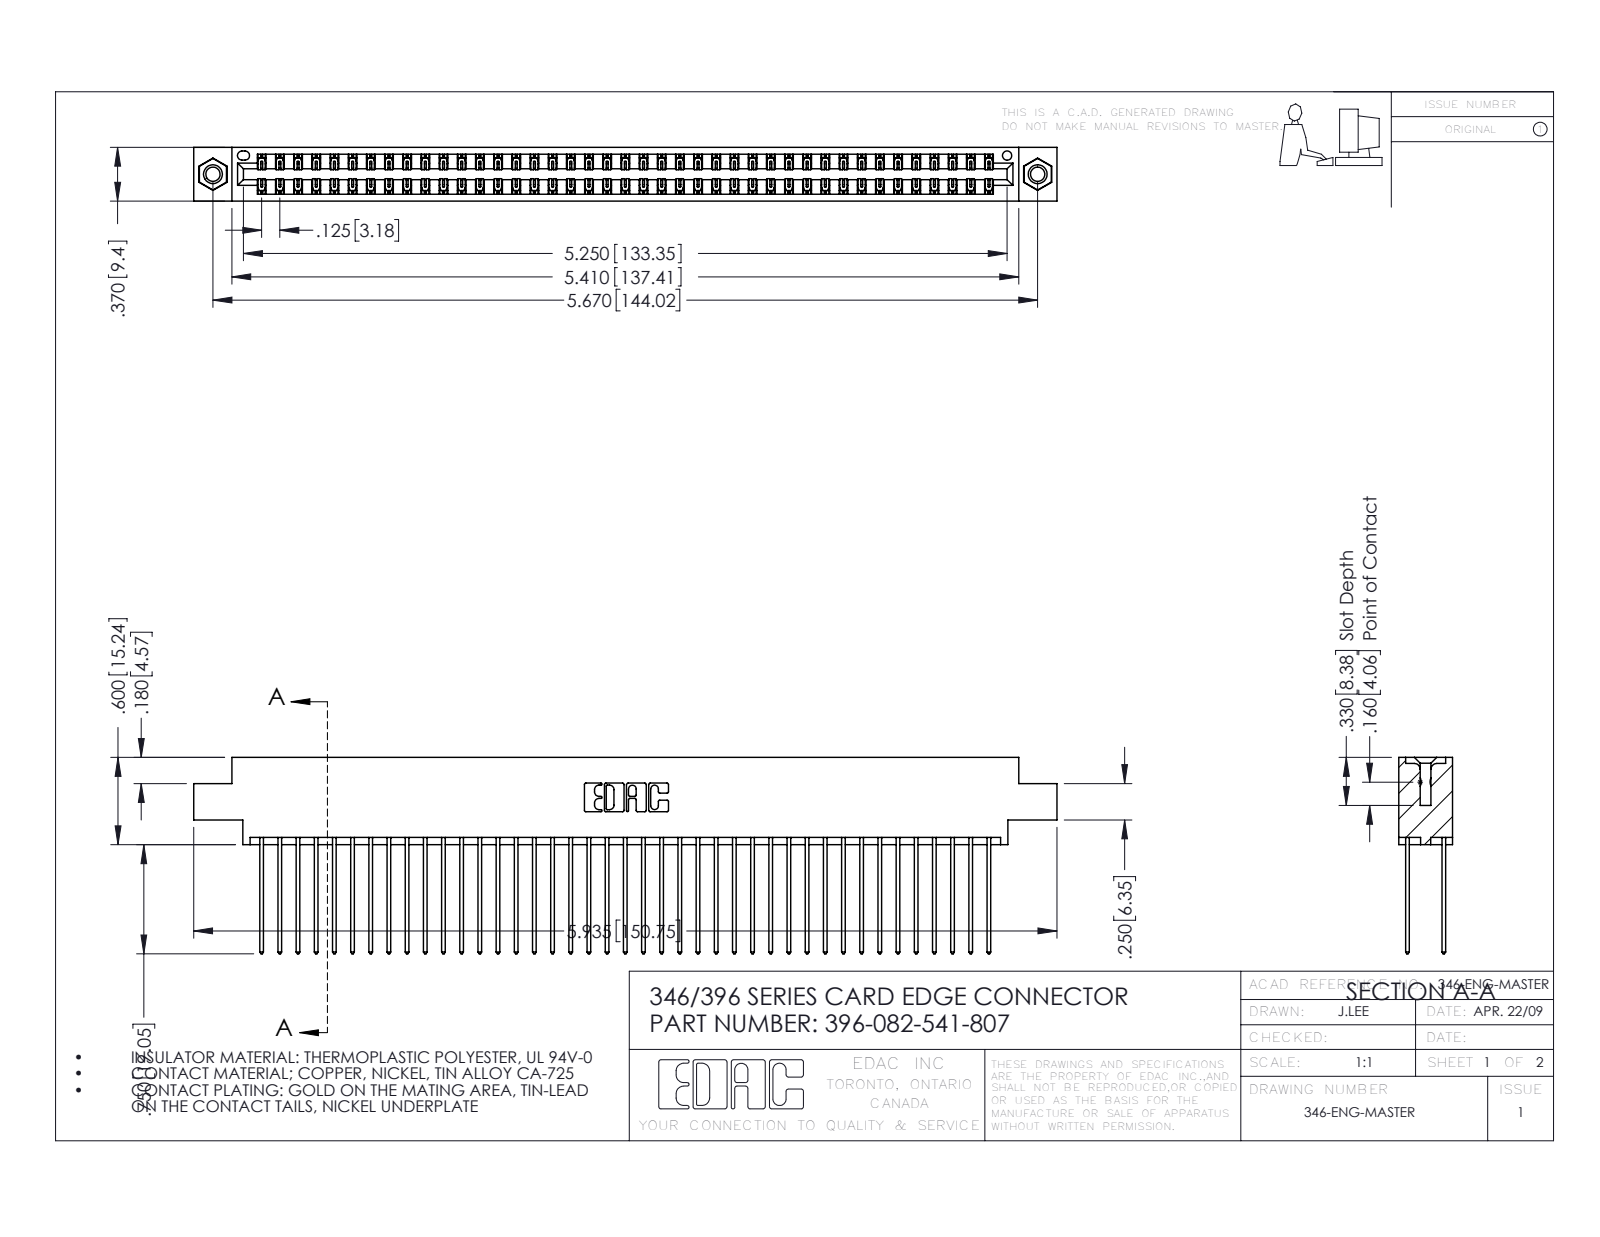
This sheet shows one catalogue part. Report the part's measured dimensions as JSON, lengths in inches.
{"part_name": "345-250-001_345-250-005-103; 345-292-001_345-293-141; 396-082-541-807; 346 Part_0.170 Offset - 0.156 Dia-TI", "step_written_by": "SolidWorks 2016 (CONFIG_CONTROL_DESIGN)", "units": "inches", "bodies": {"solids": 85, "faces": 4450, "planar": 2982, "cylindrical": 1452, "other": 16}, "overall_size": [5.935, 1.35, 0.37], "volume_in3": 0.915, "surface_area_in2": 35.75, "round_holes": [[0.098, 2], [0.125, 2], [0.156, 2], [0.064, 1]], "round_bosses_or_shafts": [[0.155, 2]], "partial_cylinders_radius": [[0.006, 123], [0.01, 82], [0.01, 22], [0.007, 6], [0.031, 6], [0.026, 3], [0.014, 2], [0.022, 2]], "face_to_face_distances": [0.048, 0.322, 0.25, 0.072, 0.298, 0.025, 0.37, 0.275, 0.225, 0.222], "hole_center_spacings": [0.246, 5.461, 5.67]}
